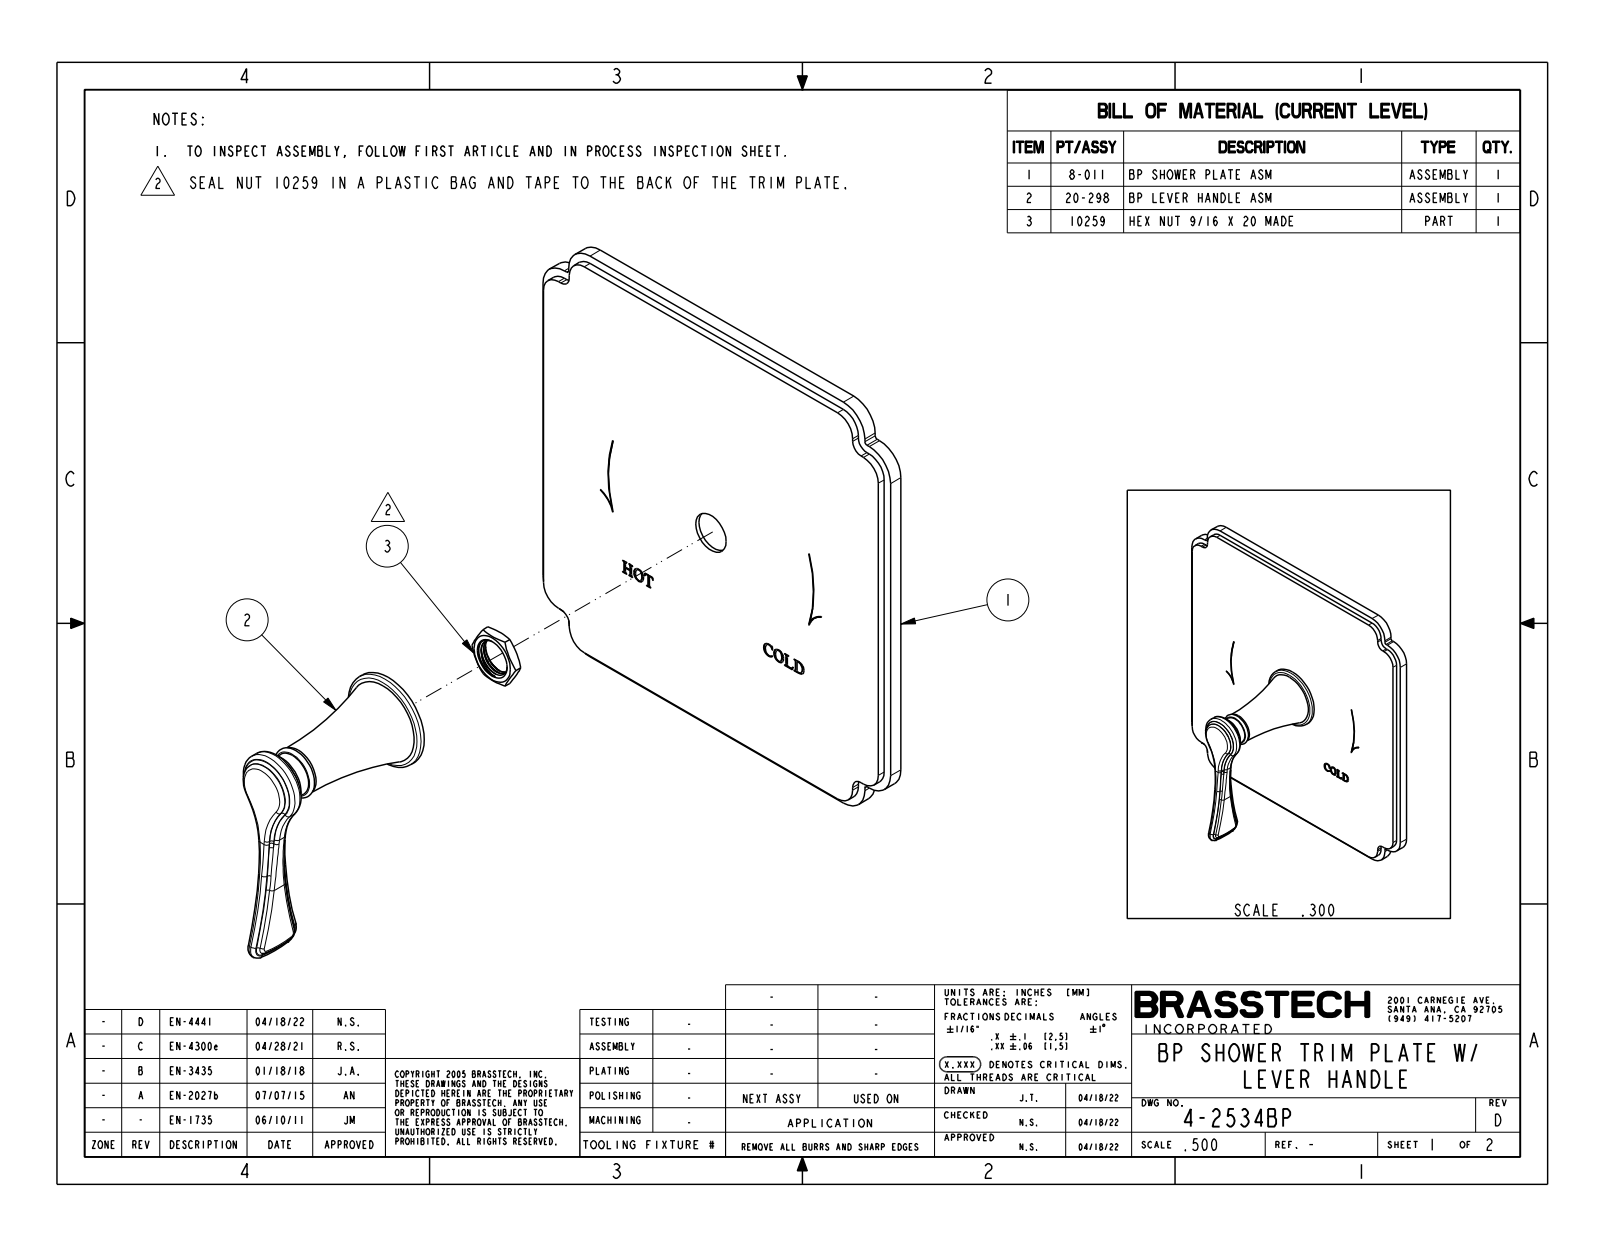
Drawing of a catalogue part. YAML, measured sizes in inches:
part_name: "4-2534BP"
step_written_by: "CREO PARAMETRIC BY PTC INC, 2018400 (CONFIG_CONTROL_DESIGN)"
units: inches
bodies: {solids: 1, faces: 356, planar: 109, cylindrical: 53, other: 194}
overall_size: [6.75, 6.75, 3]
volume: 15.31
surface_area: 106.8
round_bosses_or_shafts:
  - {diameter: 1.4, count: 1}
  - {diameter: 0.63, count: 1}
  - {diameter: 0.506, count: 1}
partial_cylinders:
  - {radius: 0.29, count: 8}
  - {radius: 0.415, count: 8}
  - {radius: 0.04, count: 4}
  - {radius: 0.165, count: 4}
  - {radius: 0.394, count: 2}
  - {radius: 0.404, count: 2}
  - {radius: 1, count: 2}
  - {radius: 1.1, count: 2}
face_to_face_distances: [0.313, 0.2, 0.113, 0.125, 6.625, 6.75, 6.5, 2.764, 2.564, 2.451]
